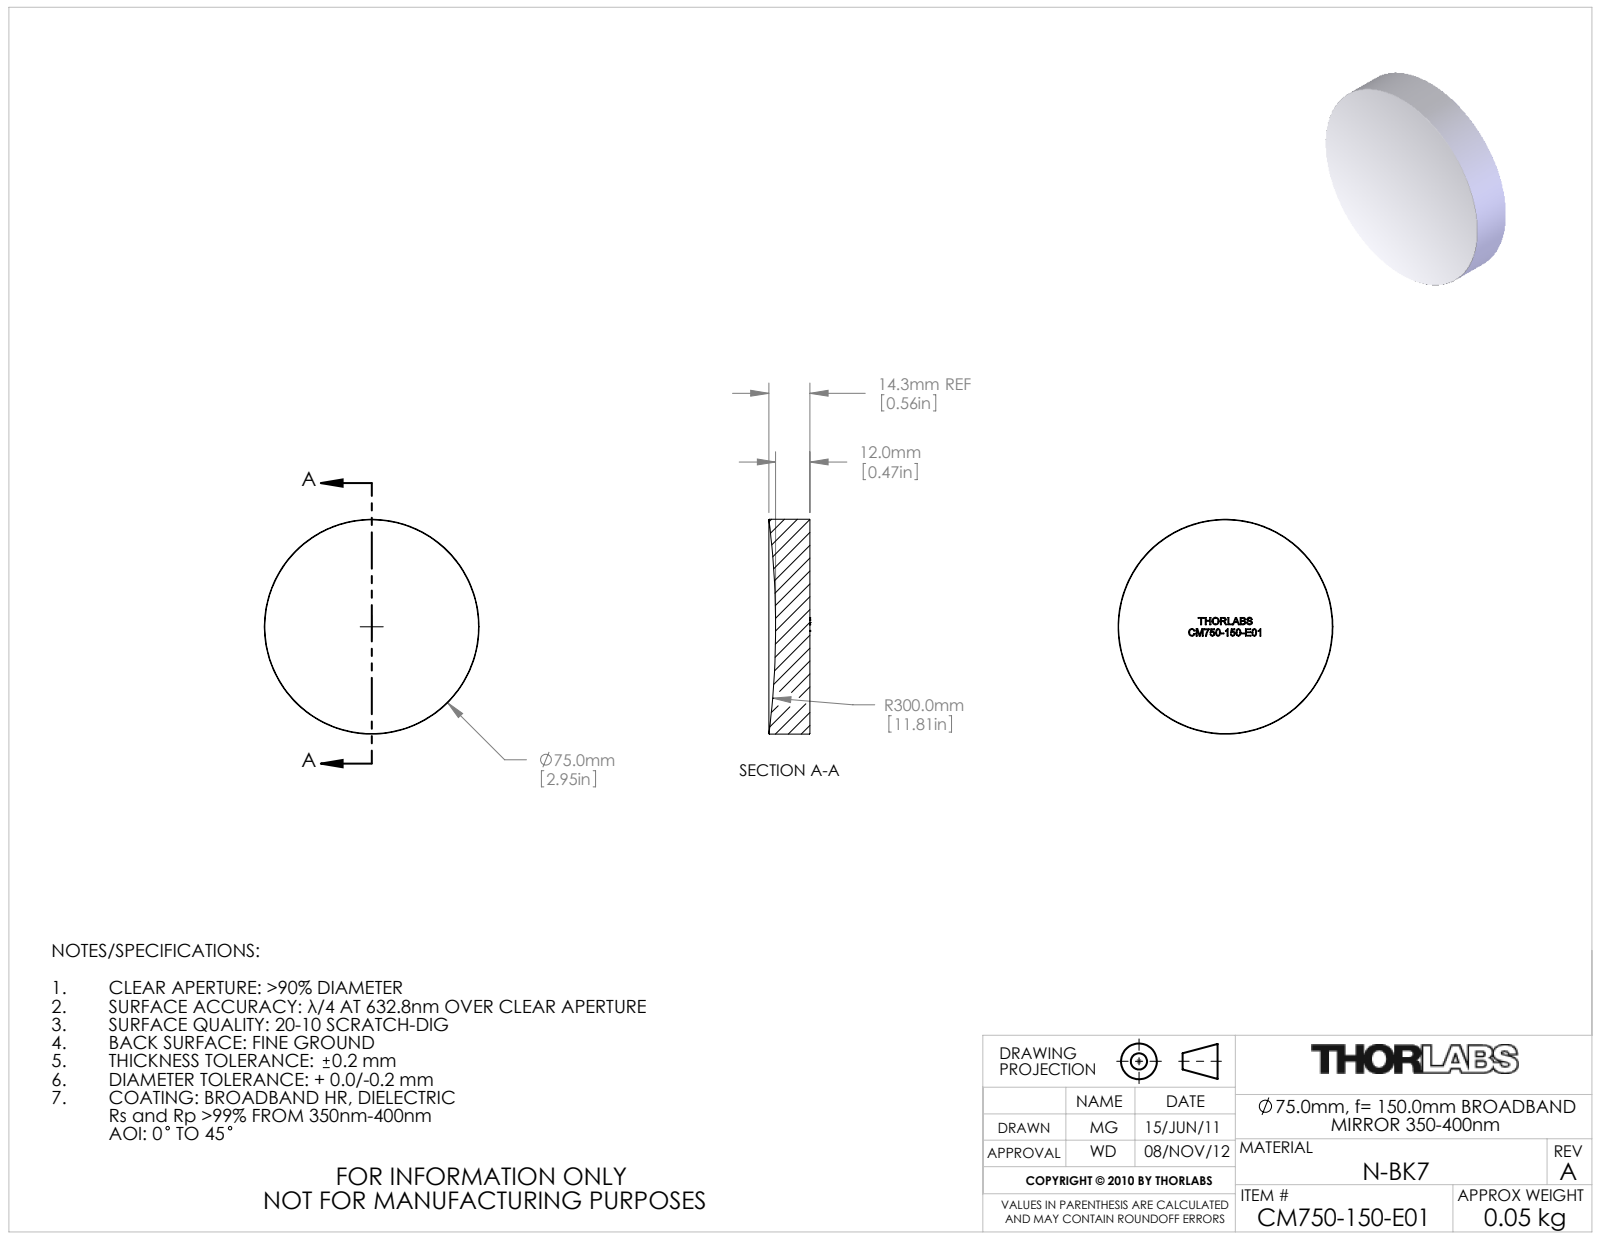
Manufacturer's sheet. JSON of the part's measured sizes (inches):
{"part_name": "22620-E0W", "step_written_by": "SolidWorks 2011 (AUTOMOTIVE_DESIGN)", "units": "inches", "bodies": {"solids": 0, "faces": 39, "planar": 31, "cylindrical": 2, "other": 6}, "overall_size": [2.953, 2.953, 0.564], "round_bosses_or_shafts": [[2.953, 1]]}
